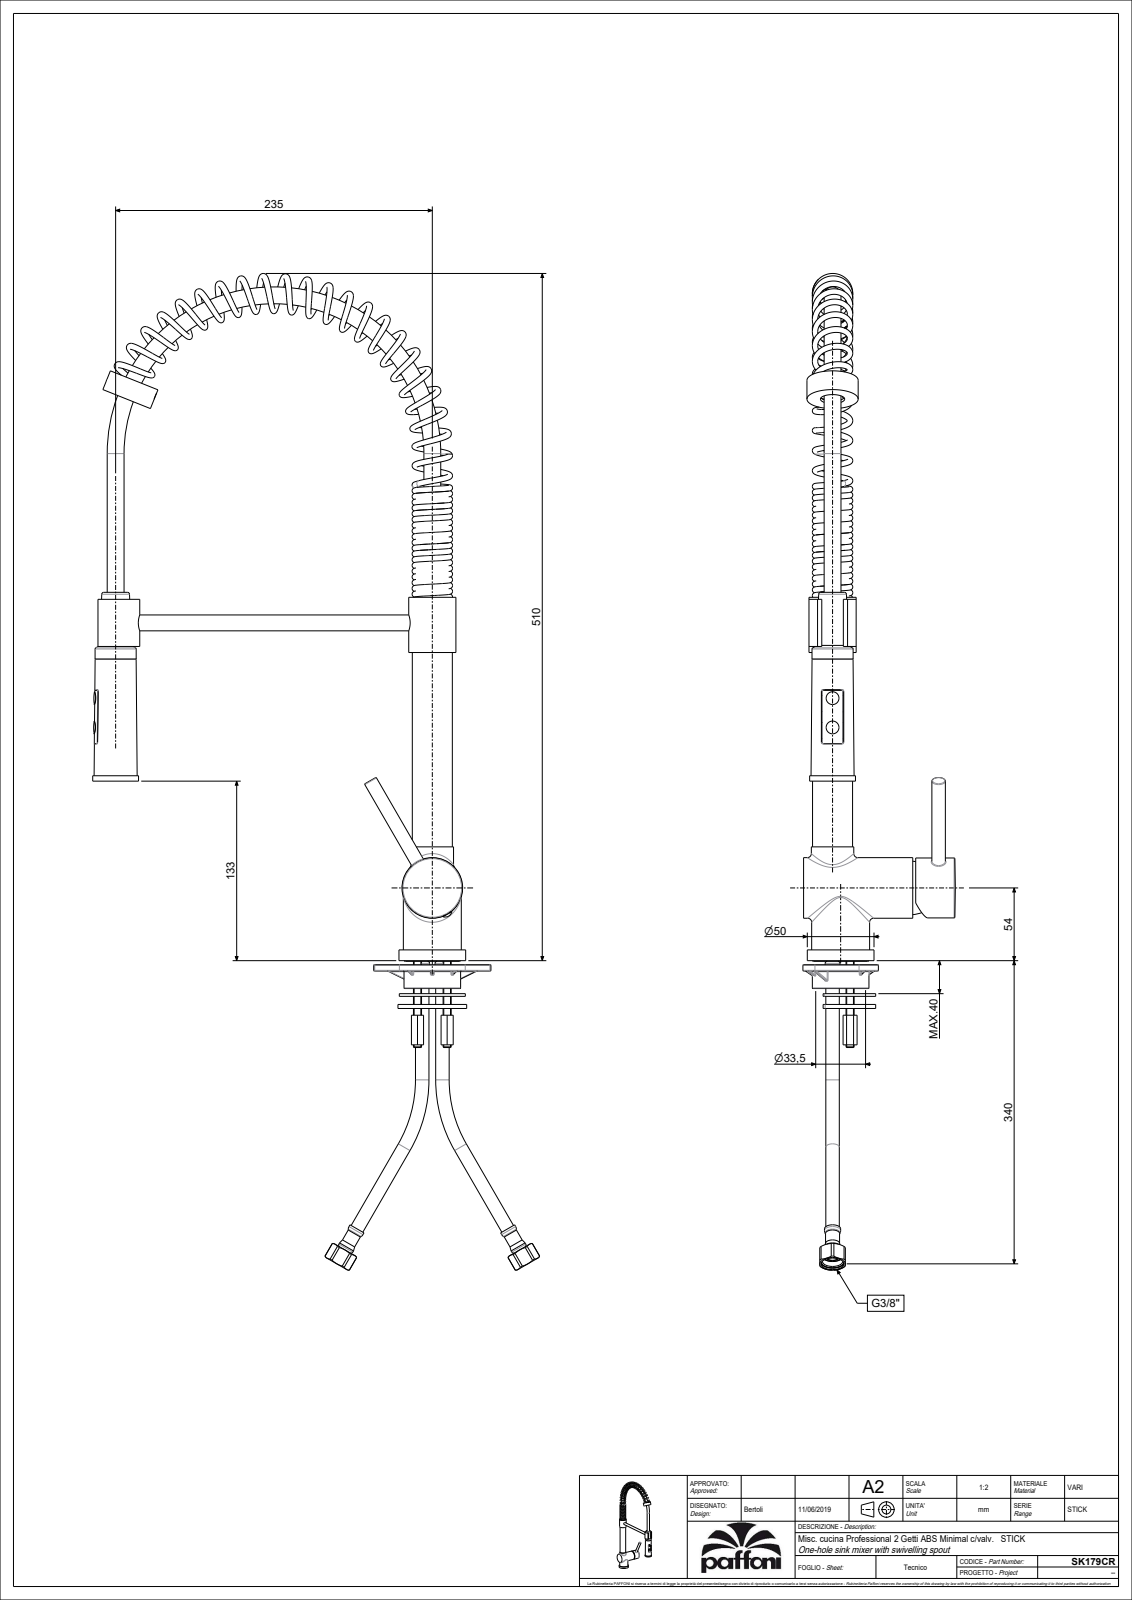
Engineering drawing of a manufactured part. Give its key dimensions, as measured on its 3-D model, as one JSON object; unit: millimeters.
{"part_name": "SK179CR", "step_written_by": "CREO PARAMETRIC BY PTC INC, 2020044 (CONFIG_CONTROL_DESIGN)", "units": "millimeters", "bodies": {"solids": 4, "faces": 3021, "planar": 1370, "cylindrical": 1052, "other": 599}, "overall_size": [510.98, 278.75, 112.59], "volume_mm3": 407967, "surface_area_mm2": 256023, "round_holes": [[0.5, 172], [7, 6], [9, 5], [12, 5], [5, 3], [11, 3], [4, 2], [6, 2], [8, 2], [9.9, 2], [18, 2], [23, 2]], "round_bosses_or_shafts": [[0.7, 16], [35, 2], [15, 2], [14, 2], [12.5, 2], [9.5, 2], [5, 2], [49.5, 1]], "partial_cylinders_radius": [[0.5, 65], [0.25, 34], [0.3, 33], [1, 16], [0.15, 11], [0.2, 8], [7, 4], [4.5, 2]], "face_to_face_distances": [1.5, 108.2, 6.5, 355, 10, 268.3, 261.8, 3, 8, 36.5], "hole_center_spacings": [0.7, 1.39, 1.83, 2.08, 2.78, 7.87, 0.69, 1.4]}
